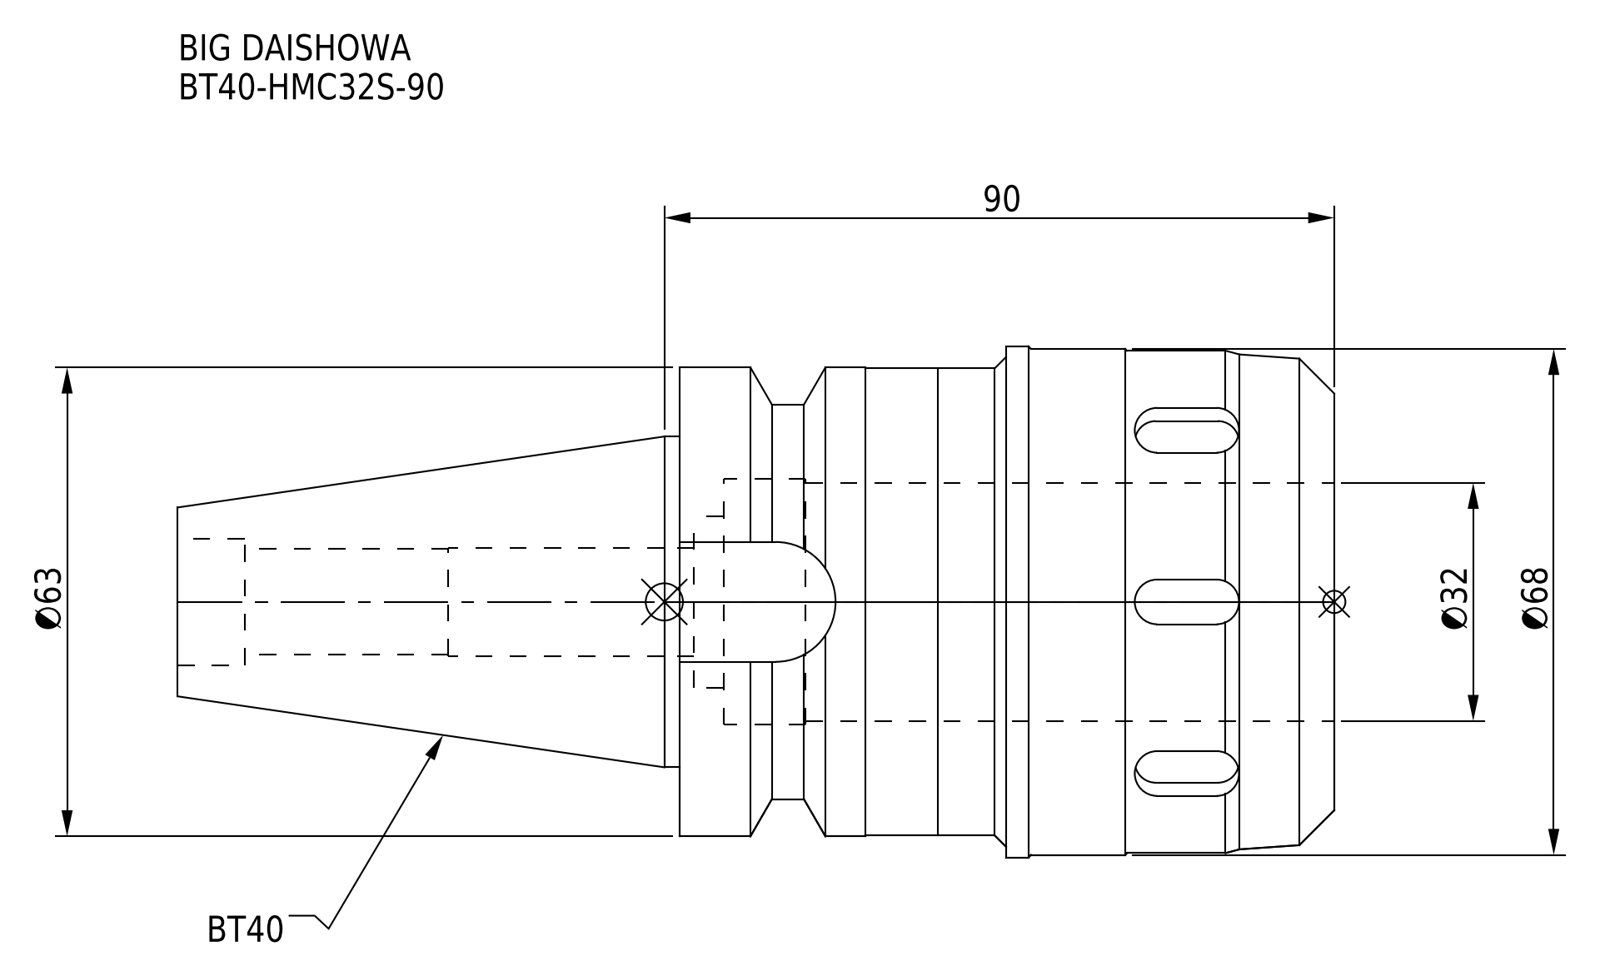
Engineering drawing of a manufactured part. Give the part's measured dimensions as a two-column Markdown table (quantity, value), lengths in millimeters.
| quantity | value |
| --- | --- |
| part name | BT40-HMC32S-90 |
| STEP written by | CREO PARAMETRIC BY PTC INC, 2016380 (AUTOMOTIVE_DESIGN) |
| units | millimeters |
| bodies | 1 solid, 104 faces (40 planar, 46 cylindrical, 18 other) |
| overall size | 155.4 × 68.7 × 68.7 |
| volume | 266 020 mm³ |
| surface area | 44 077 mm² |
| round holes (diameter × count) | 14.2 × 1, 14.5 × 1, 17 × 1, 23 × 1, 32 × 1, 33 × 1 |
| round bosses / shafts (diameter × count) | 68.7 × 1, 68 × 1, 67.5 × 1, 63 × 1, 62.8 × 1, 53 × 1, 44.45 × 1 |
| partial cylindrical surfaces (radius × count) | 3 × 12, 8.05 × 1 |
| main face-to-face distances | 88, 6, 82, 63, 45, 44.1, 37.9, 43.9, 155.4, 111.3 |
